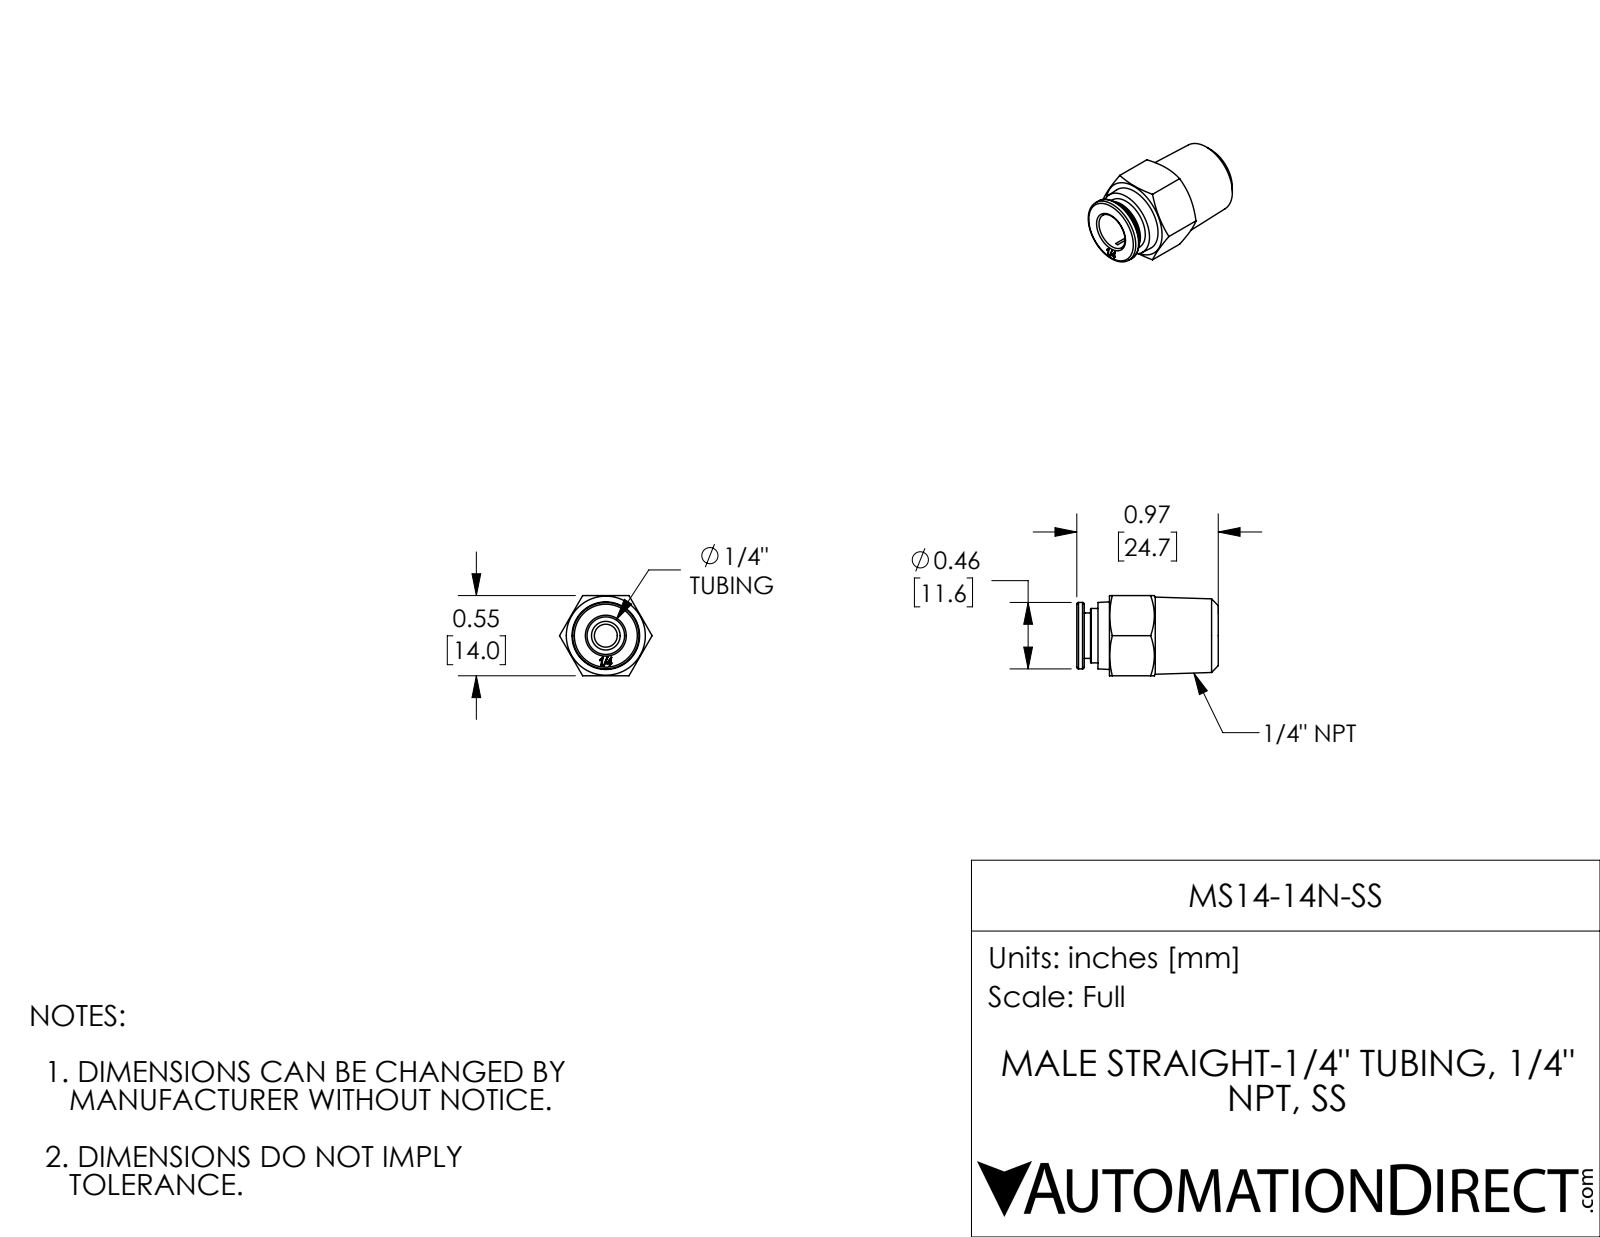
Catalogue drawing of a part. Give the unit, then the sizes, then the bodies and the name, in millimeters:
Units: millimetres
Overall size (bounding box): 24.7 × 16.2 × 14
Round holes (diameter × count): ⌀4 ×1, ⌀6.6 ×1, ⌀8.1 ×1
Round bosses / shafts (diameter × count): ⌀11.6 ×1, ⌀9.5 ×1, ⌀8 ×1
Main face-to-face distances: 14, 24.7, 1.3, 2.4, 23.4, 19, 4.4, 5.7, 21, 2
Volume: 2 640 mm³ · Surface area: 1 877 mm²
Bodies: 1 solid, 87 faces (47 planar, 12 cylindrical, 28 other)
Part name (STEP PRODUCT): MS14-14N-SS
STEP written by: SolidWorks 2017 (AUTOMOTIVE_DESIGN)
